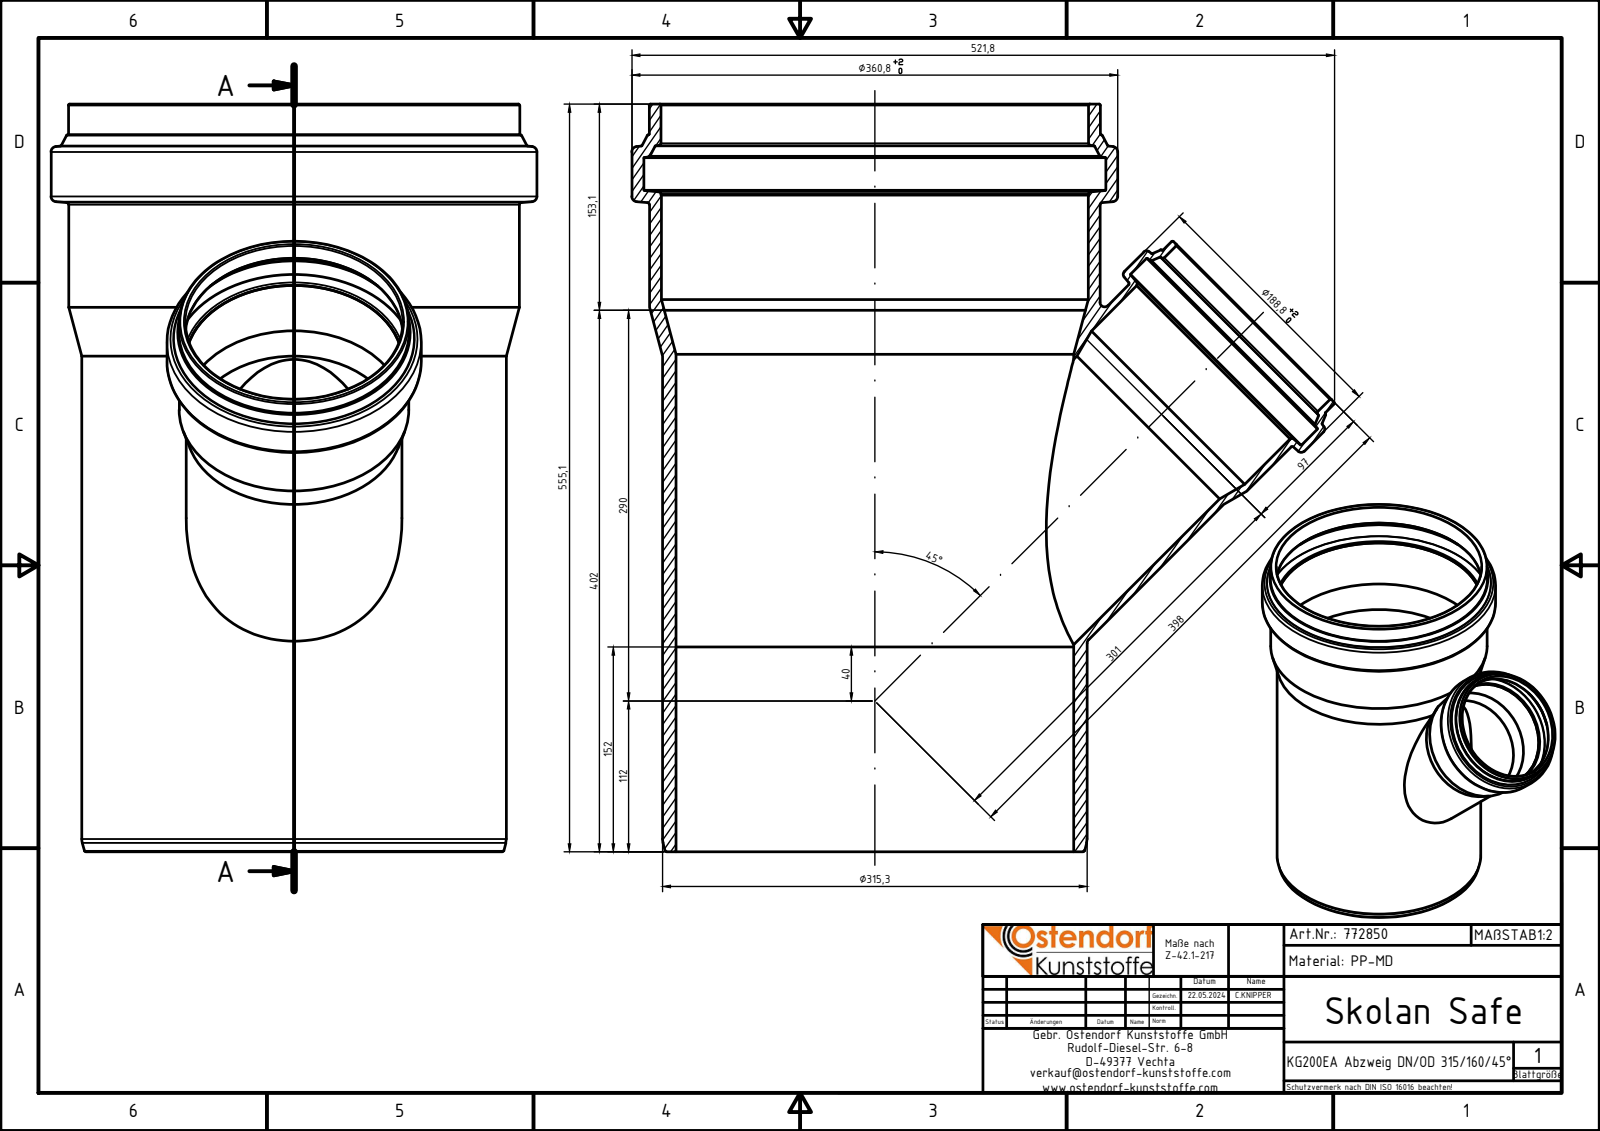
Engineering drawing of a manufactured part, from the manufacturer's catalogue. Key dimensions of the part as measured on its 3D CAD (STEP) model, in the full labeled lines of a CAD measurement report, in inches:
Part name (STEP PRODUCT): 772850z
STEP written by: Autodesk Inventor 2024 (AUTOMOTIVE_DESIGN)
Units: inches
Bodies: 1 solid, 78 faces (5 planar, 18 cylindrical, 55 other)
Overall size (bounding box): 21.854 × 20.542 × 14.205
Volume: 349.2 in³ · Surface area: 2 027 in²
Round holes (diameter × count): ⌀6.35 ×2, ⌀5.898 ×1, ⌀6.339 ×1, ⌀7.063 ×1, ⌀11.626 ×1, ⌀12.484 ×1, ⌀12.5 ×1, ⌀13.512 ×1
Round bosses / shafts (diameter × count): ⌀14.205 ×1, ⌀13.193 ×1, ⌀13.177 ×1, ⌀12.413 ×1, ⌀7.433 ×1, ⌀6.72 ×1, ⌀6.709 ×1, ⌀6.307 ×1
Main face-to-face distances: 21.854, 19.197, 2.657, 1.673
